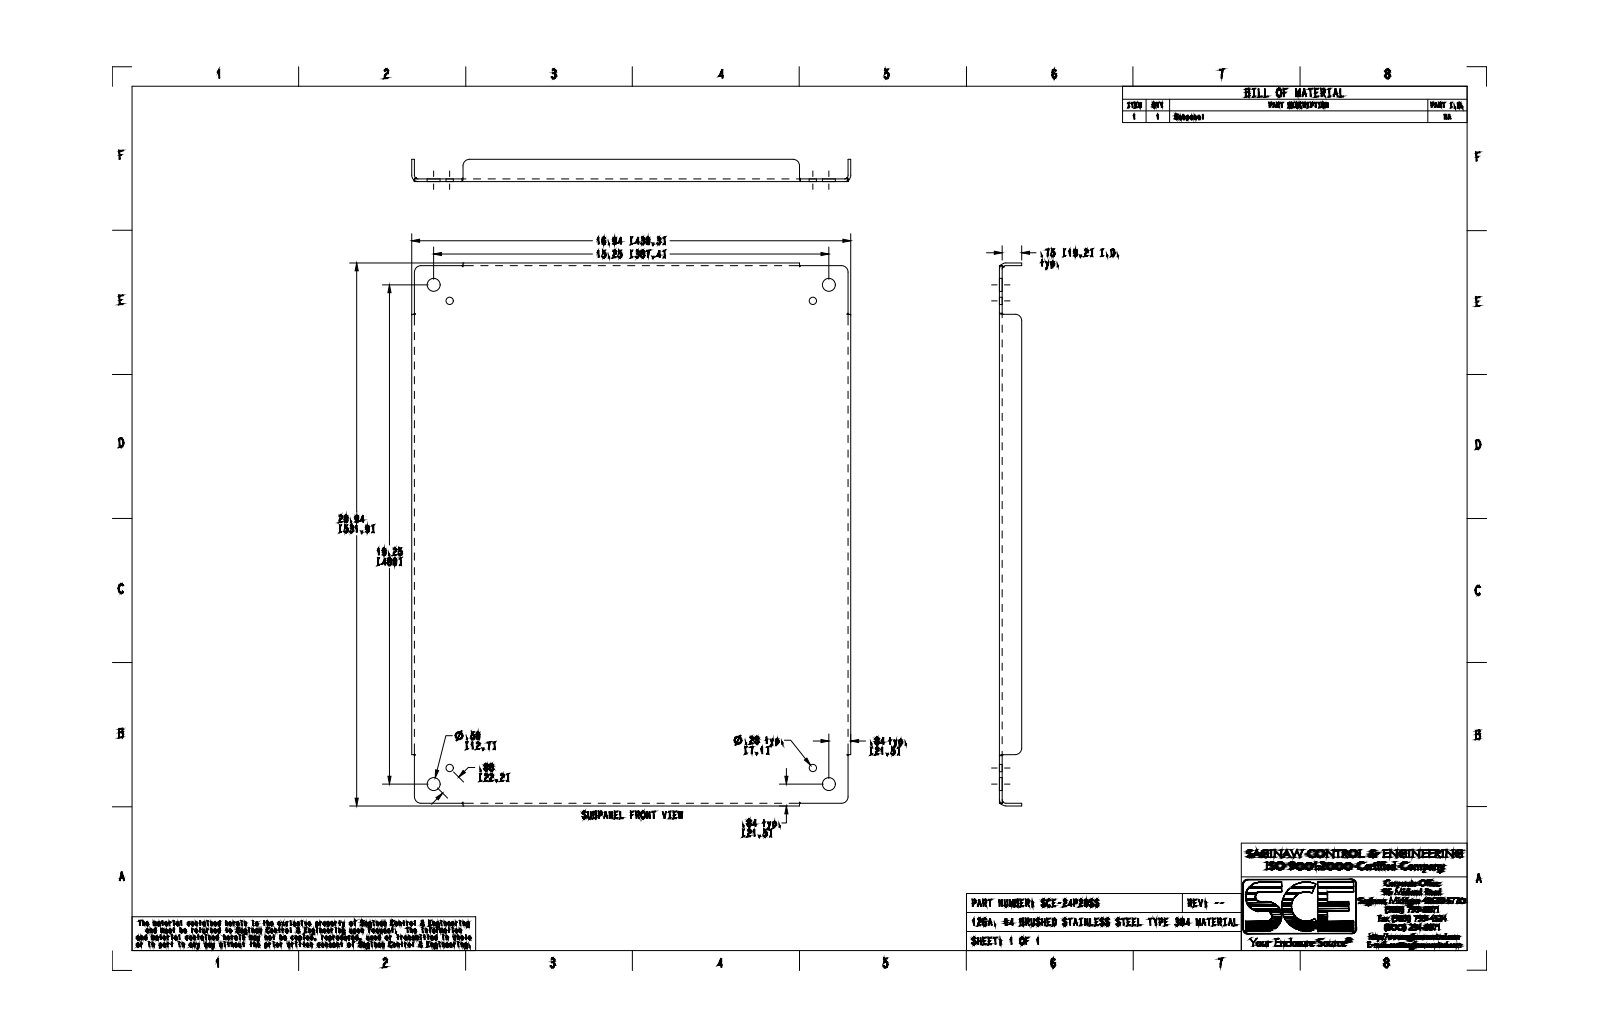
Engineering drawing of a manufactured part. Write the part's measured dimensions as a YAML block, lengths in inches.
part_name: "SCE-24P20SS"
step_written_by: "SolidWorks 2019 (CONFIG_CONTROL_DESIGN)"
units: inches
bodies: {solids: 1, faces: 82, planar: 30, cylindrical: 28, other: 24}
overall_size: [20.941, 16.941, 0.858]
volume: 40.79
surface_area: 793.7
round_holes:
  - {diameter: 0.281, count: 4}
  - {diameter: 0.5, count: 4}
partial_cylinders:
  - {radius: 0.25, count: 8}
  - {radius: 0.246, count: 4}
  - {radius: 0.142, count: 2}
  - {radius: 0.143, count: 2}
face_to_face_distances: [0.104, 16.838, 20.838, 16.734, 16.942, 20.734, 20.942, 0.754, 0.858, 1.979]
hole_center_spacings: [0.875, 14.646, 18.643, 23.692, 14.014, 15.252, 18.014, 19.252]
